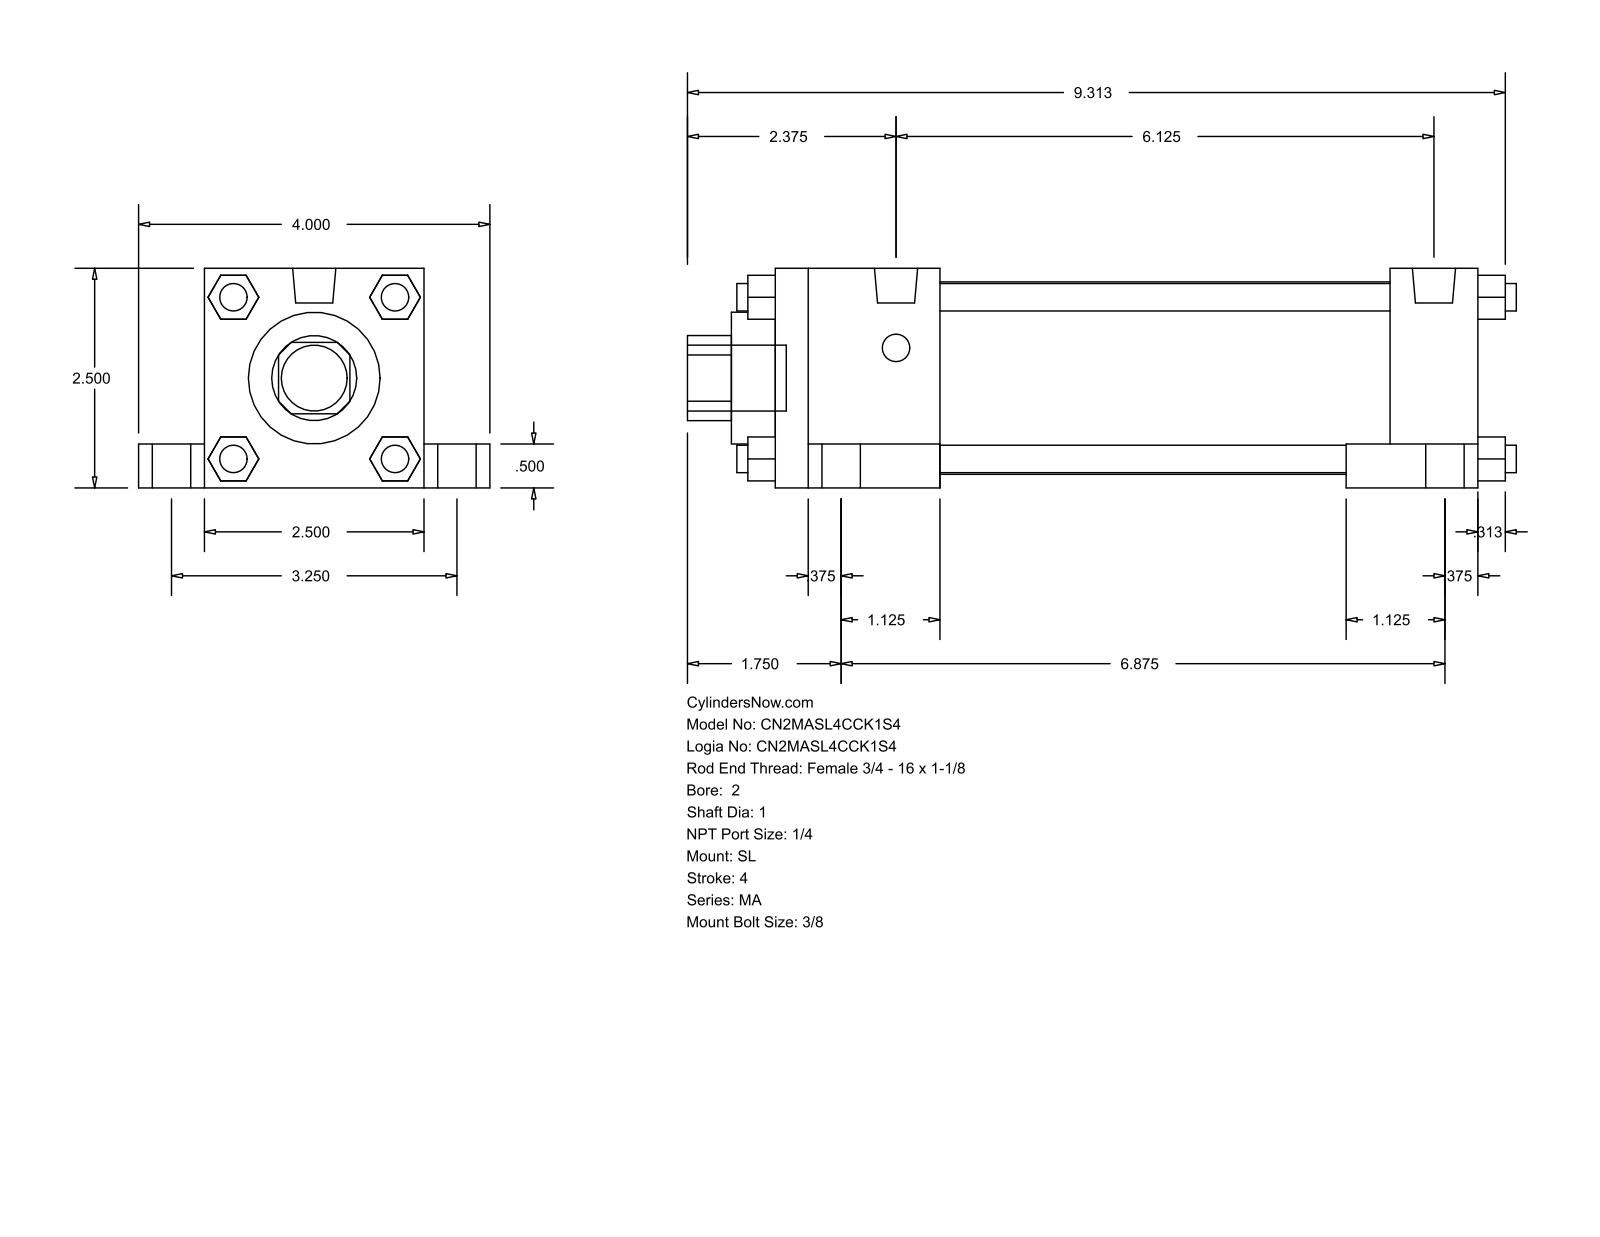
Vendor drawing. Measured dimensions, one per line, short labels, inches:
name: MA_SL__0200_1
written by: GSSL Pune (CONFIG_CONTROL_DESIGN)
unit: in
bodies: 0 solids, 148 faces (112 planar, 36 cylindrical, 0 other)
size: 9.437 × 4 × 2.5
holes: 1× ⌀1, 1× ⌀1.5, 1× ⌀2.19
bosses: 8× ⌀0.313, 4× ⌀0.687, 4× ⌀0.437, 2× ⌀0.492, 1× ⌀0.75
rounds: 1× R0.484
face distances: 2.5, 0.5, 8, 0.75, 3.25, 1, 2, 1.875, 6.125, 7
